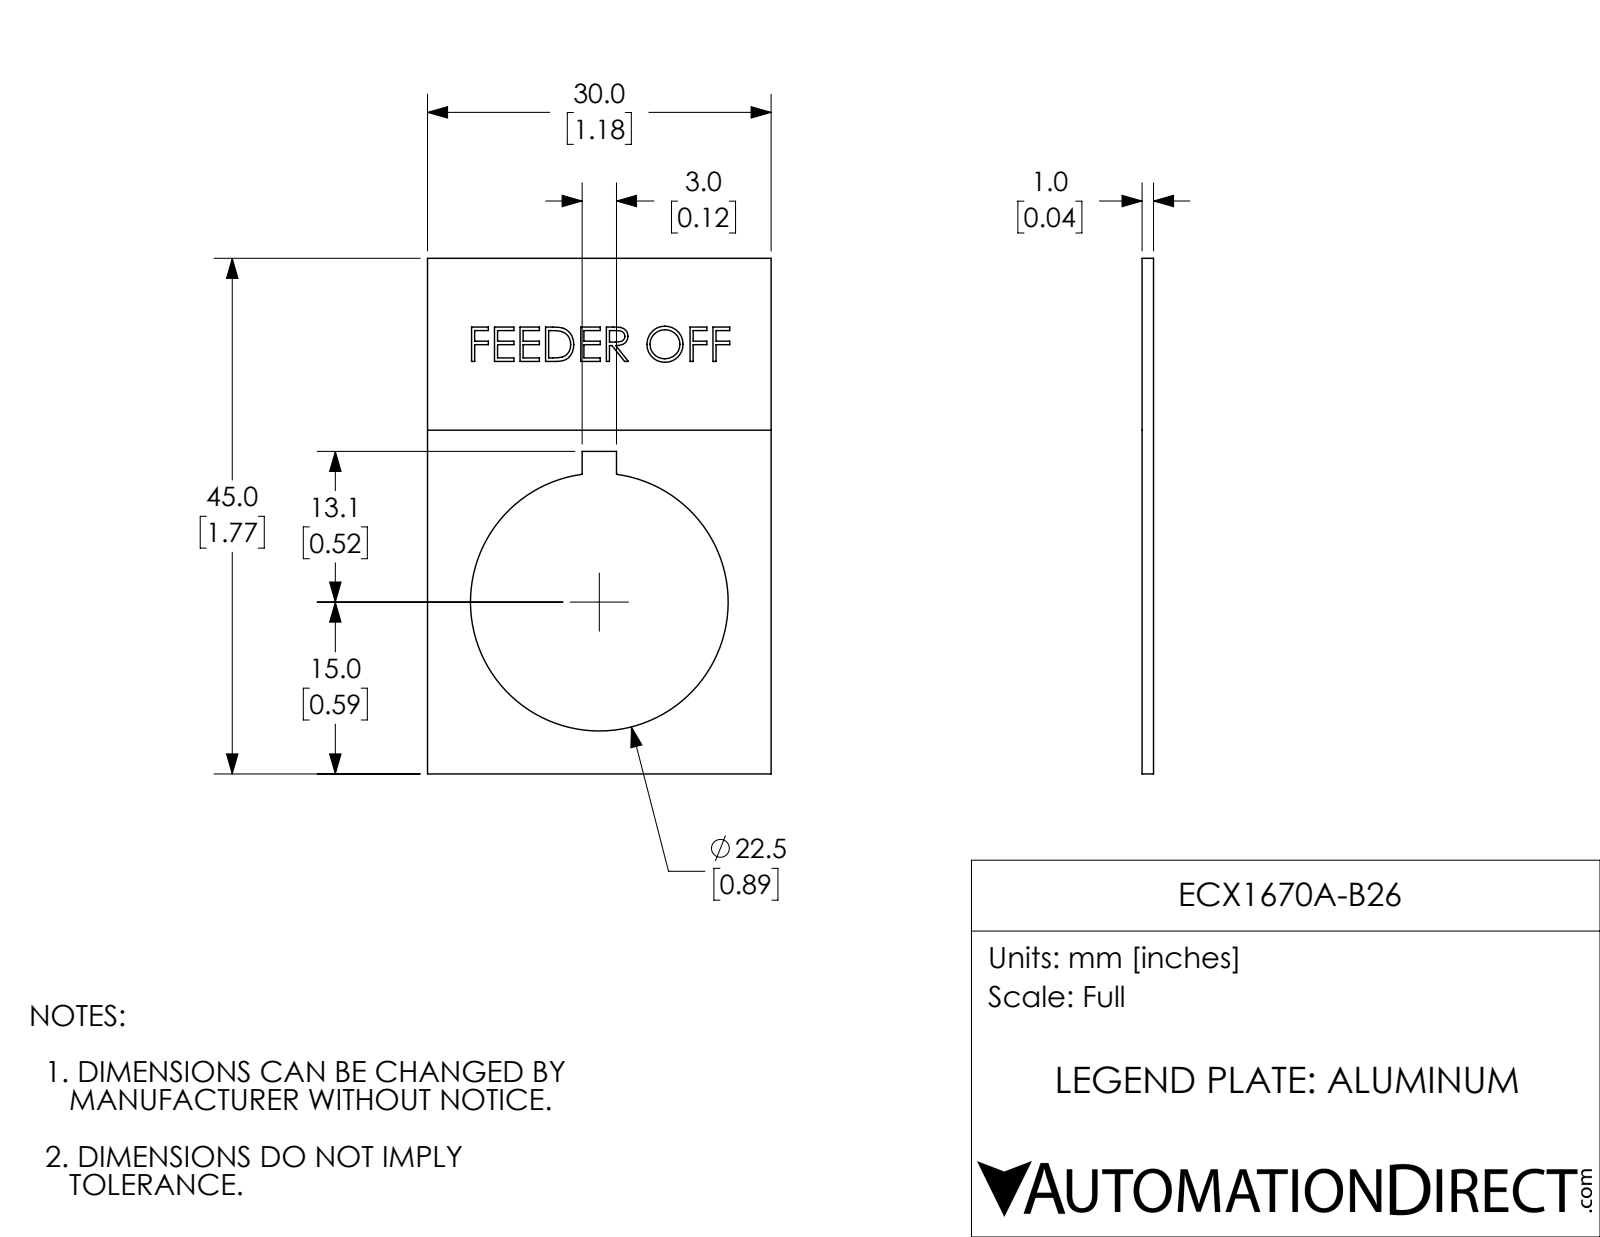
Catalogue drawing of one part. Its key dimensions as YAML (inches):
part_name: "ECX1670A-B26"
step_written_by: "SolidWorks 2017 (AUTOMOTIVE_DESIGN)"
units: inches
bodies: {solids: 1, faces: 128, planar: 105, cylindrical: 3, other: 20}
overall_size: [1.772, 1.181, 0.039]
volume: 0.058
surface_area: 3.288
round_holes:
  - {diameter: 0.886, count: 1}
face_to_face_distances: [0.039, 1.181, 1.772, 0.038, 0.531, 0.65, 1.108, 0.663, 0.118, 0.012]
